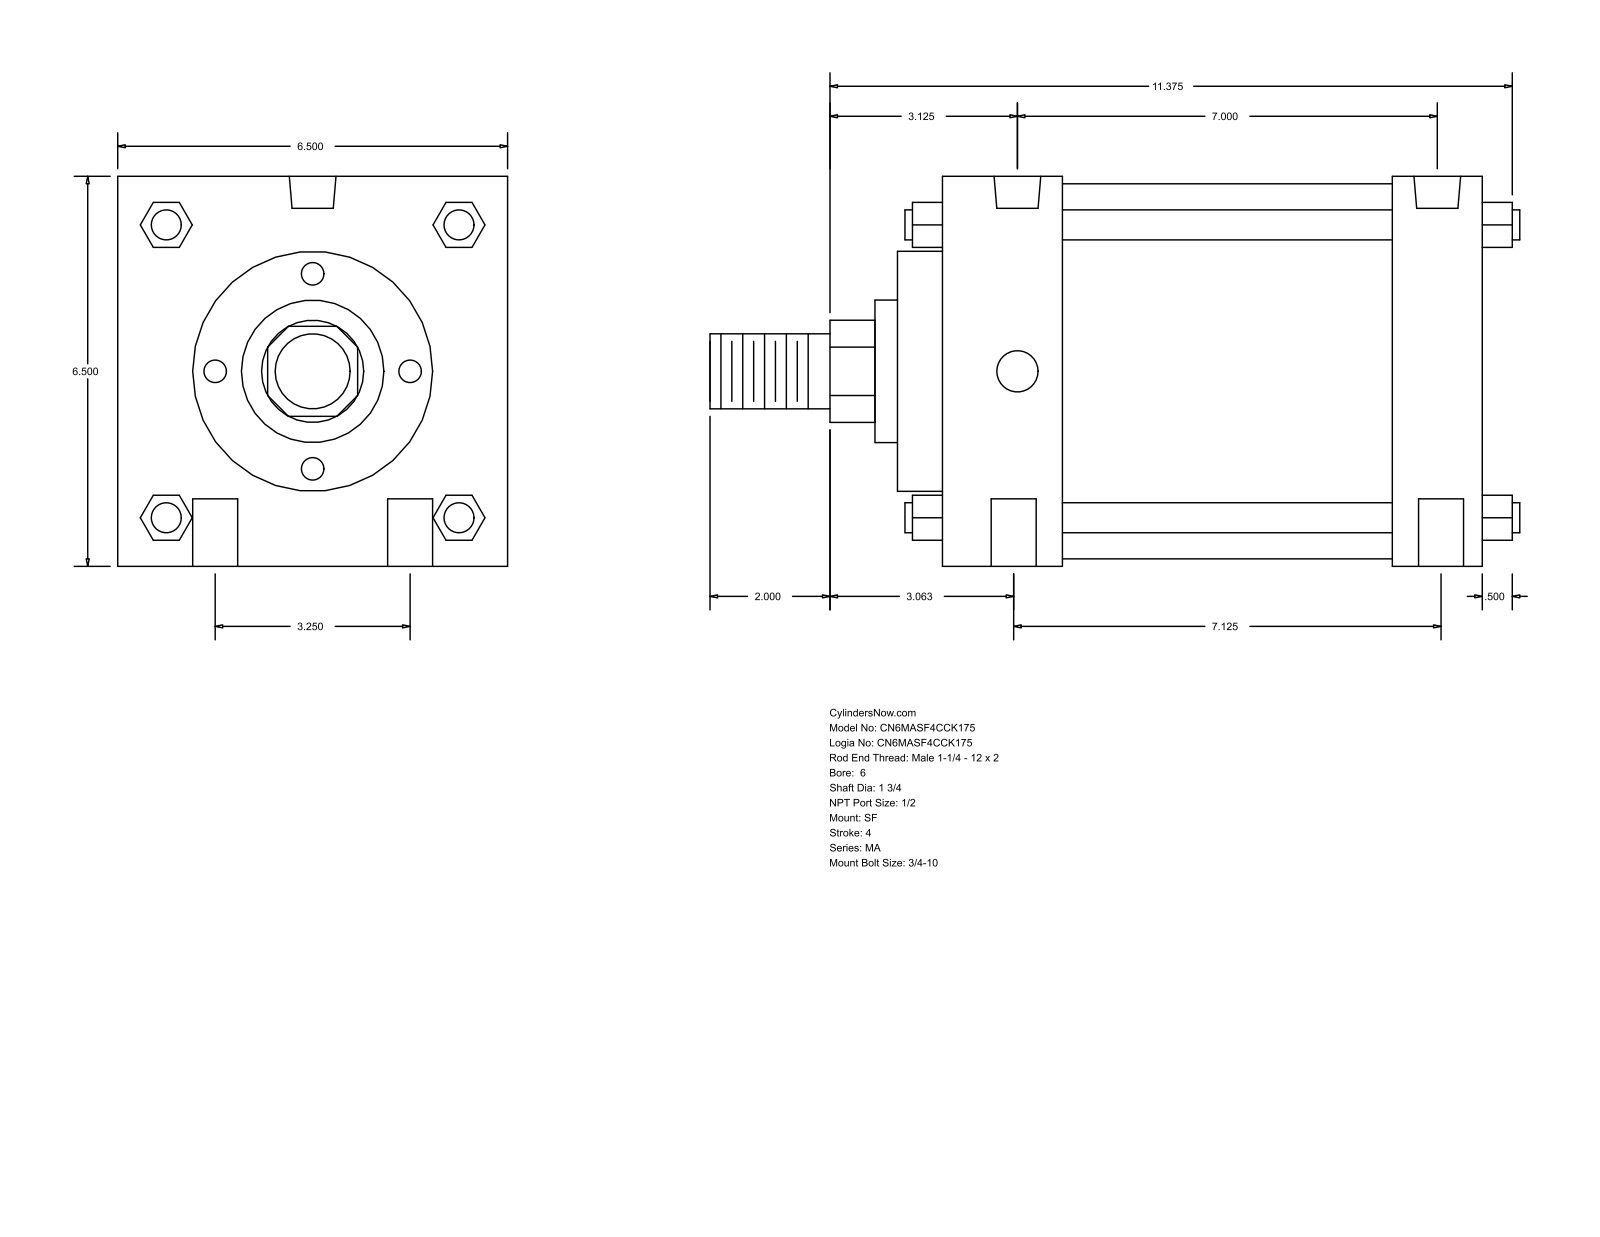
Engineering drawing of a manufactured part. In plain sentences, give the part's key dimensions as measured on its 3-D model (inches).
The part is named "MA_SF__0600_1.75". Its 3-D file was written by "GSSL Pune (CONFIG_CONTROL_DESIGN)". It is 0 solids with 126 faces: 95 planar, 31 cylindrical and 0 other. Overall it measures 13.5 by 6.5 by 6.5 inches. Round holes: 4 of diameter 0.75, 2 of diameter 0.687, 2 of diameter 0.778. Round bosses or shafts: 4 of diameter 0.5, 1 of diameter 6.25, 1 of diameter 4, 1 of diameter 2.375, 1 of diameter 1.75, 1 of diameter 1.25. Partial cylindrical surfaces (rounded edges, fillets, slot ends): 1 of radius 0.852. The main face-to-face distances are 6.5, 9, 0.75, 2, 7.5, 1.5, 5.5, 7, 2.75, 8.25. The hole center spacings are 1.626, 3.25, 7, 7.125, 7.247, 7.247, 7.831.
